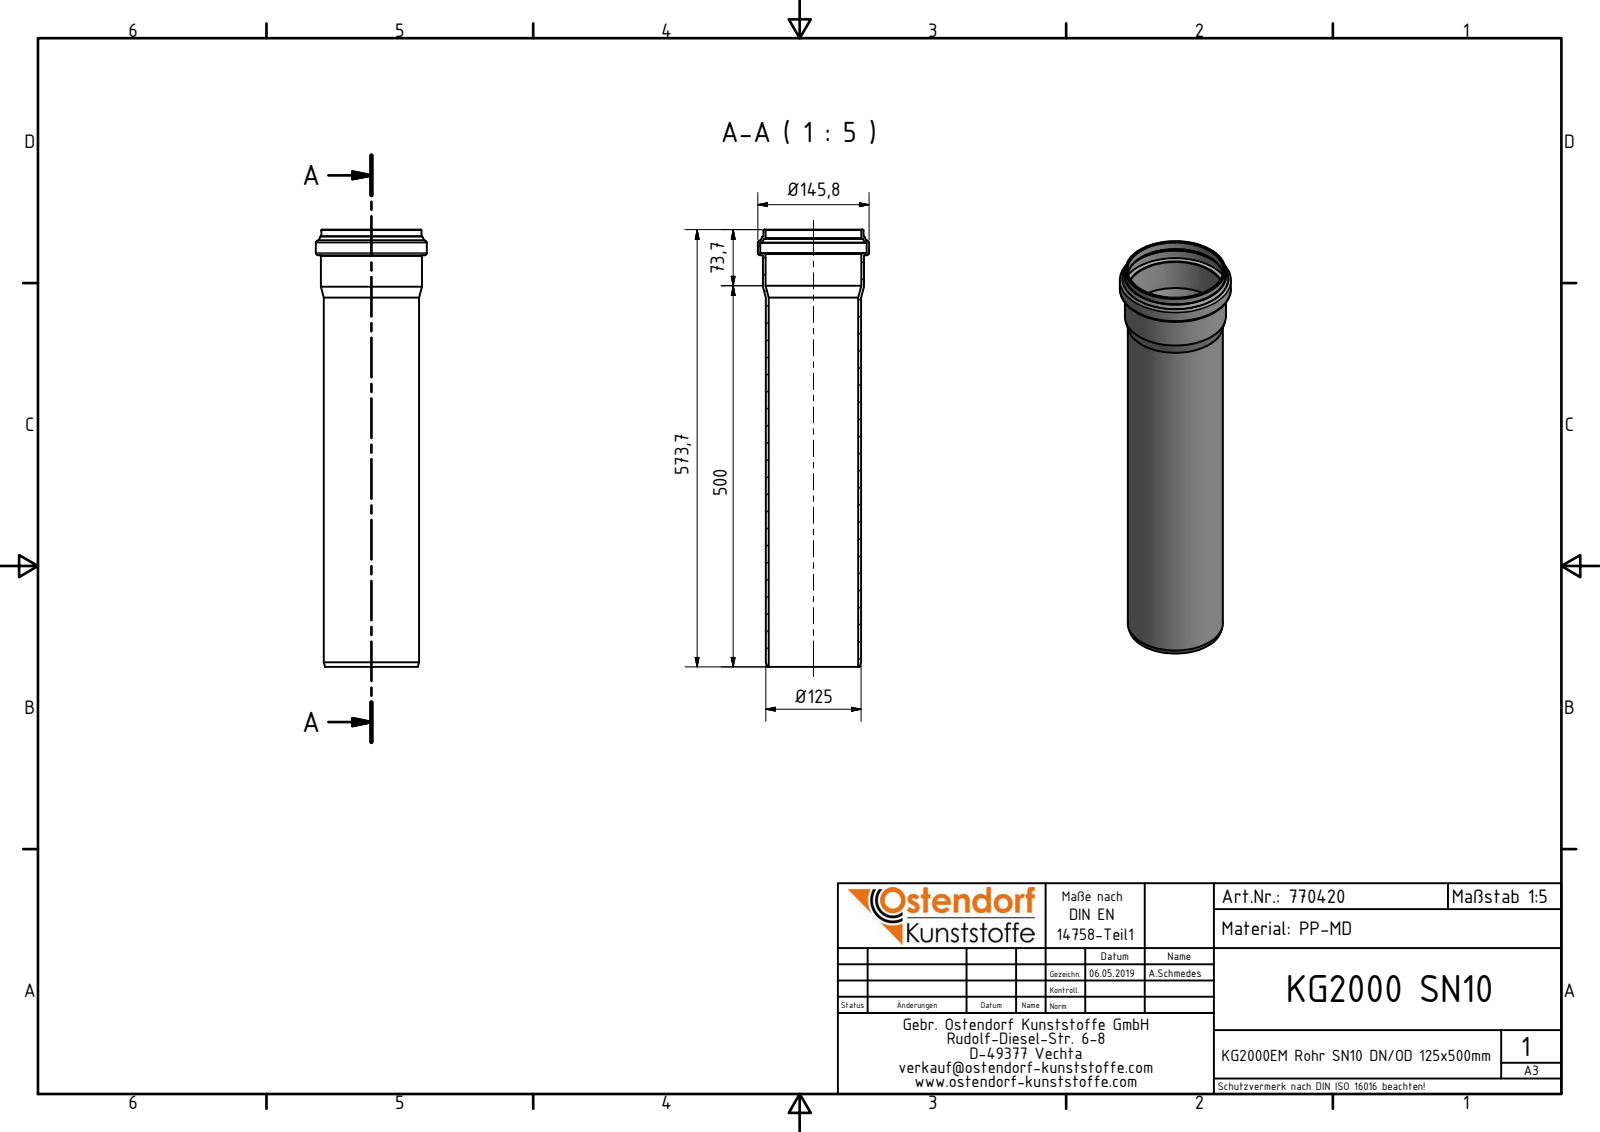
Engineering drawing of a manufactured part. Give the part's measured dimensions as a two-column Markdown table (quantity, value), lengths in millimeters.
| quantity | value |
| --- | --- |
| part name | 770420 KG2000EM Rohr SN10 DN-OD125x500 |
| STEP written by | Autodesk Inventor 2016 (AUTOMOTIVE_DESIGN) |
| units | millimeters |
| bodies | 1 solid, 35 faces (5 planar, 8 cylindrical, 22 other) |
| overall size | 573.7 × 145.8 × 145.8 |
| volume | 855 294 mm³ |
| surface area | 452 467 mm² |
| round holes (diameter × count) | 117.2 × 1, 125.5 × 1, 139.8 × 1 |
| round bosses / shafts (diameter × count) | 145.8 × 1, 132.7 × 1, 131.5 × 1, 125 × 1 |
| main face-to-face distances | 540, 573.7, 33.7, 564.87, 24.87, 8.83, 559.5, 19.5, 5.37, 14.2 |
